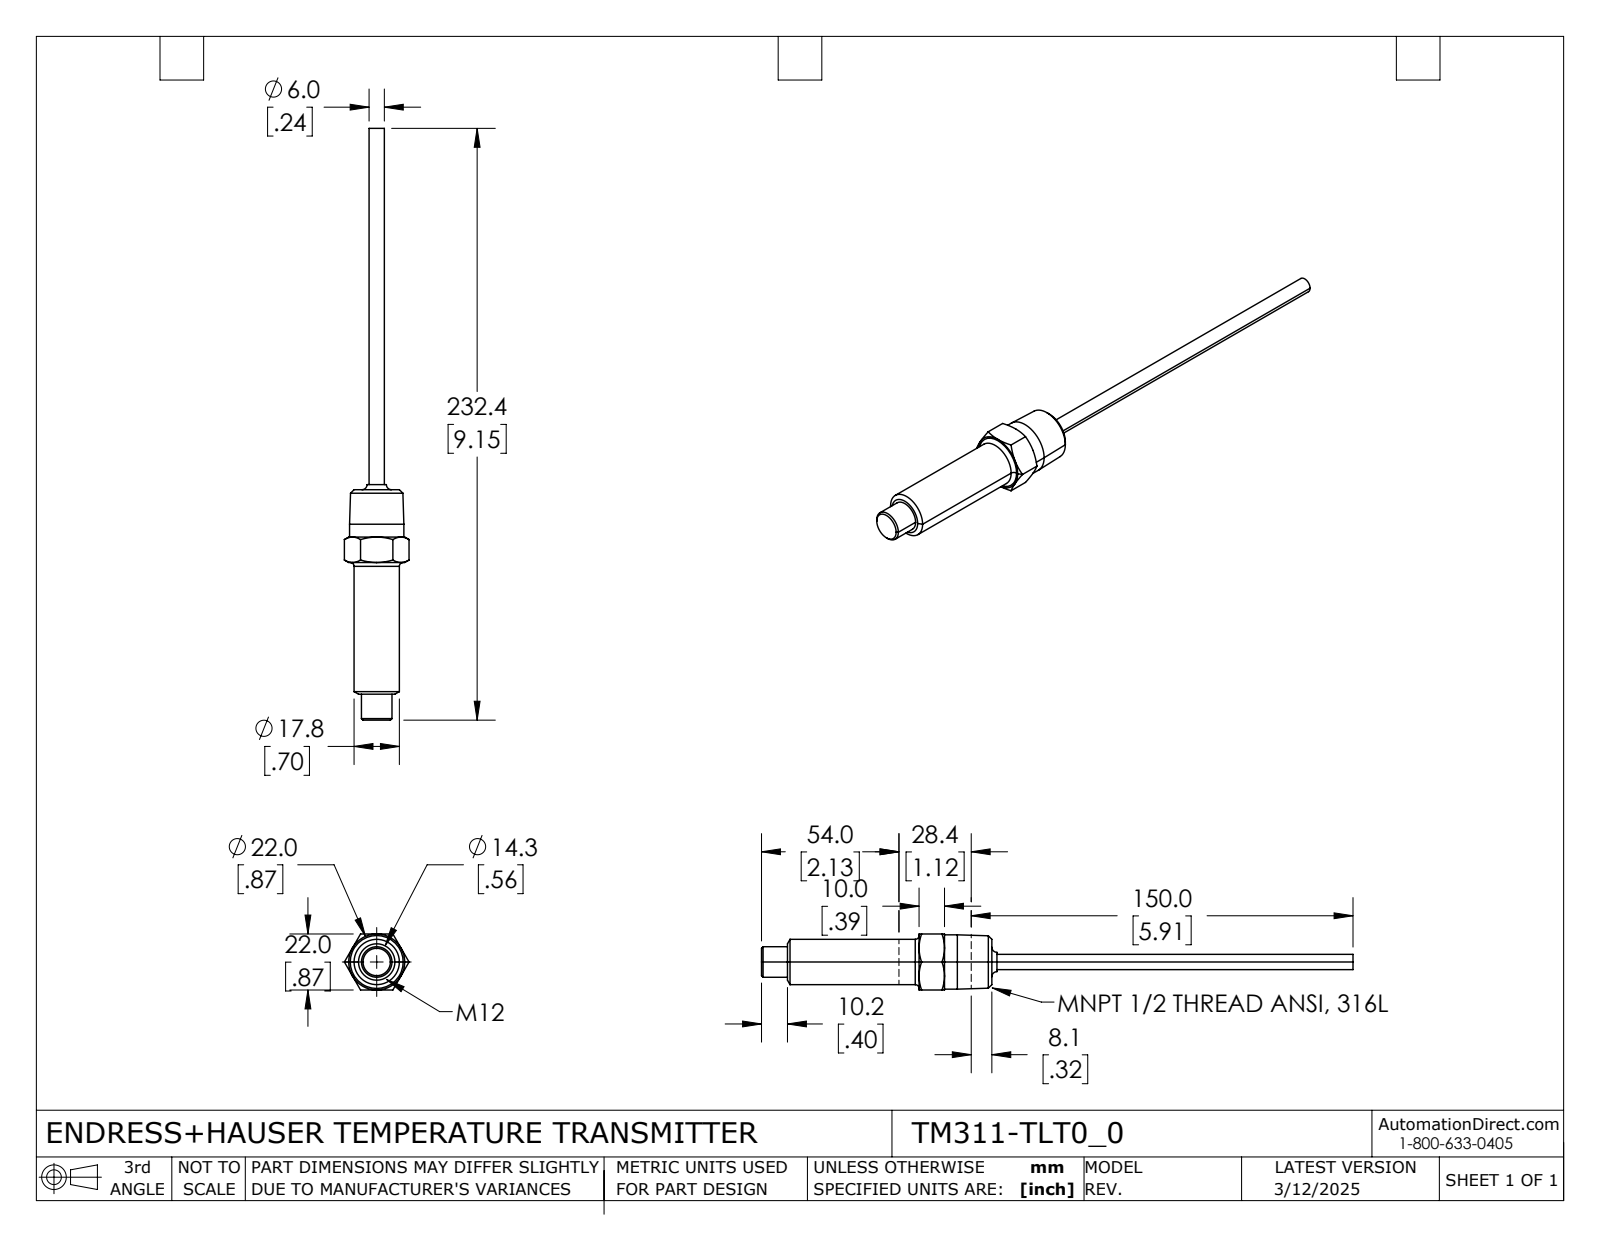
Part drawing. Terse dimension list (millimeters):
name: TM311-TLT0_0
written by: SolidWorks 2021 (AUTOMOTIVE_DESIGN)
unit: mm
bodies: 1 solid, 49 faces (13 planar, 8 cylindrical, 28 other)
size: 232.4 × 25.4 × 22
volume: 28 640 mm³; area: 8 561 mm²
bosses: 1× ⌀21.3, 1× ⌀17.8, 1× ⌀12, 1× ⌀6
face distances: 22, 90.5, 80.3, 10.2, 28.6, 51.7, 61.9, 141.9, 170.5, 222.2
